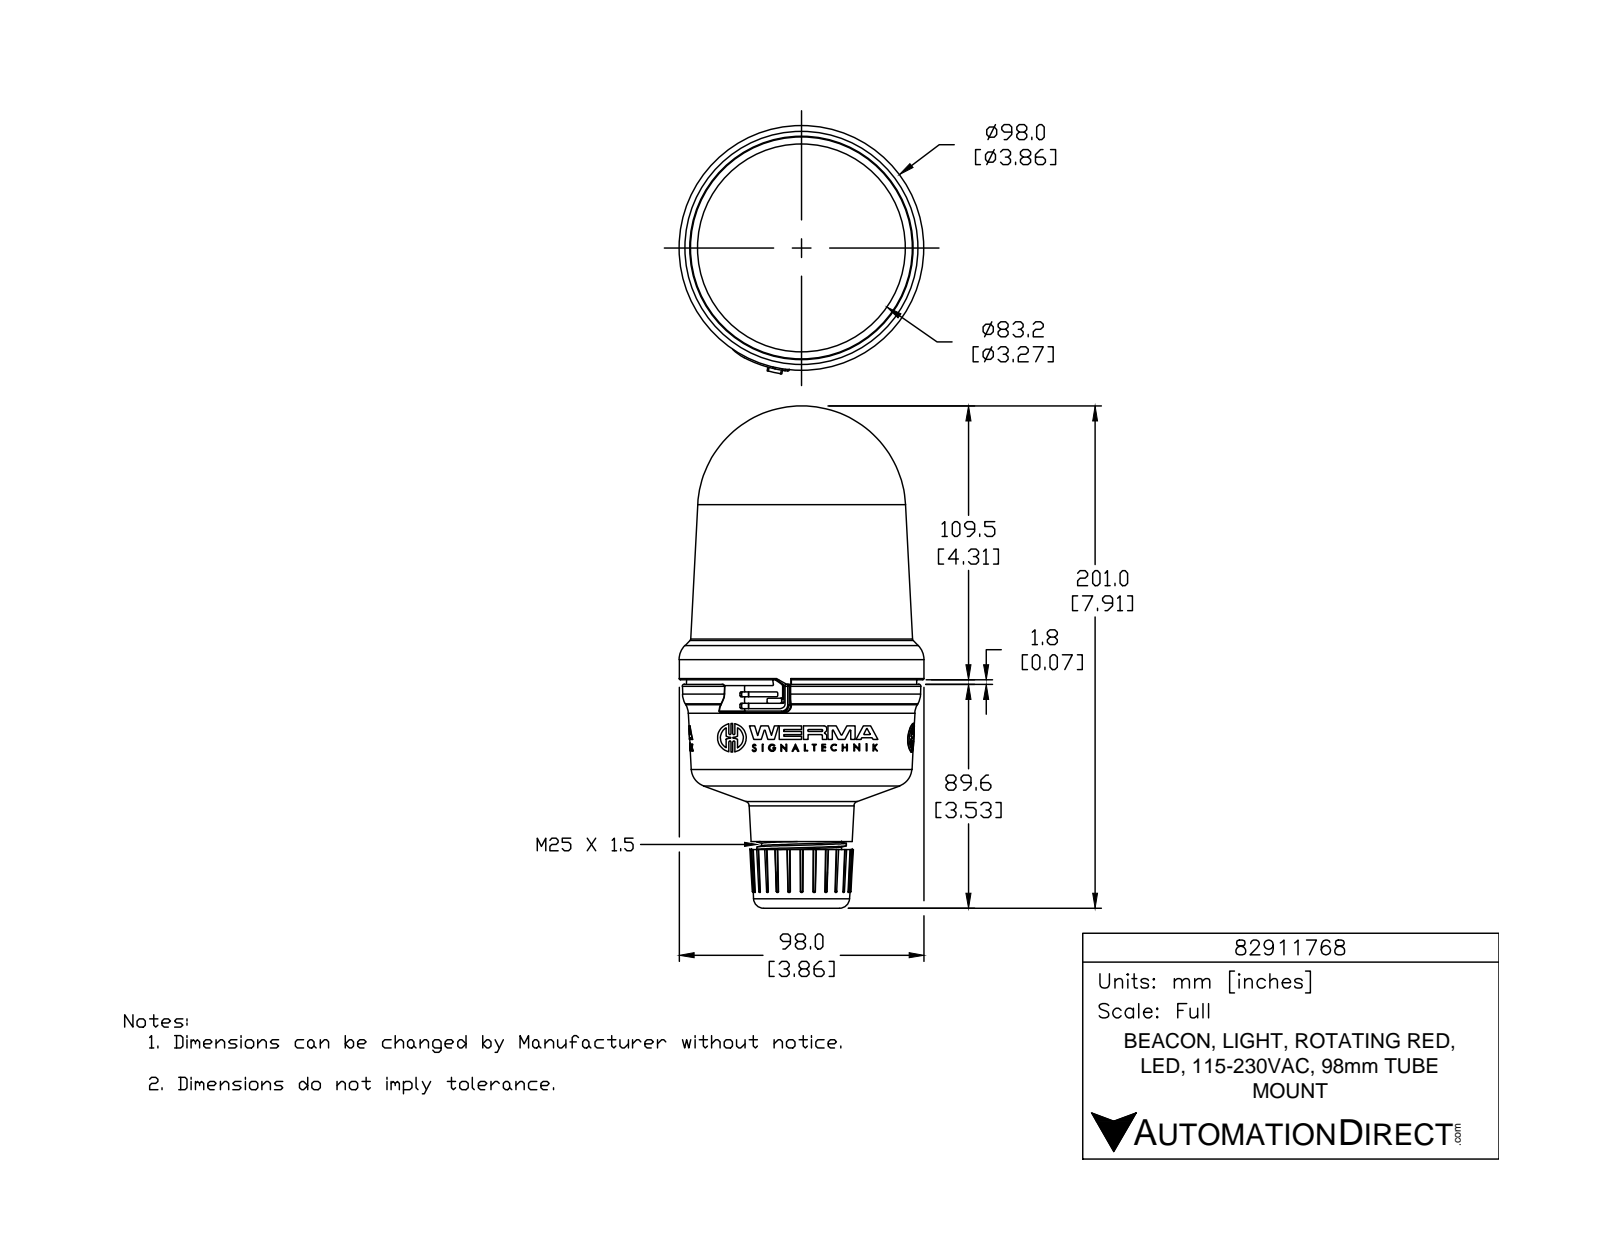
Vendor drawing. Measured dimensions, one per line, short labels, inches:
name: 82911768
written by: SolidWorks 2015 (AUTOMOTIVE_DESIGN)
unit: in
bodies: 1 solid, 1006 faces (554 planar, 189 cylindrical, 263 other)
size: 7.914 × 3.912 × 3.858
volume: 54.7 in³; area: 91.39 in²
holes: 3× ⌀0.078, 1× ⌀1.013, 1× ⌀1.024
bosses: 3× ⌀0.452, 3× ⌀0.113, 1× ⌀3.858, 1× ⌀1.409, 1× ⌀1.261
rounds: 12× R0.02, 9× R0.007, 6× R0.007, 6× R0.016, 6× R0.016, 6× R0.016, 6× R0.262, 3× R0.006
face distances: 2.214, 0.462, 2.676, 0.335, 0.127, 2.548, 2.603, 2.476, 2.141, 0.073
